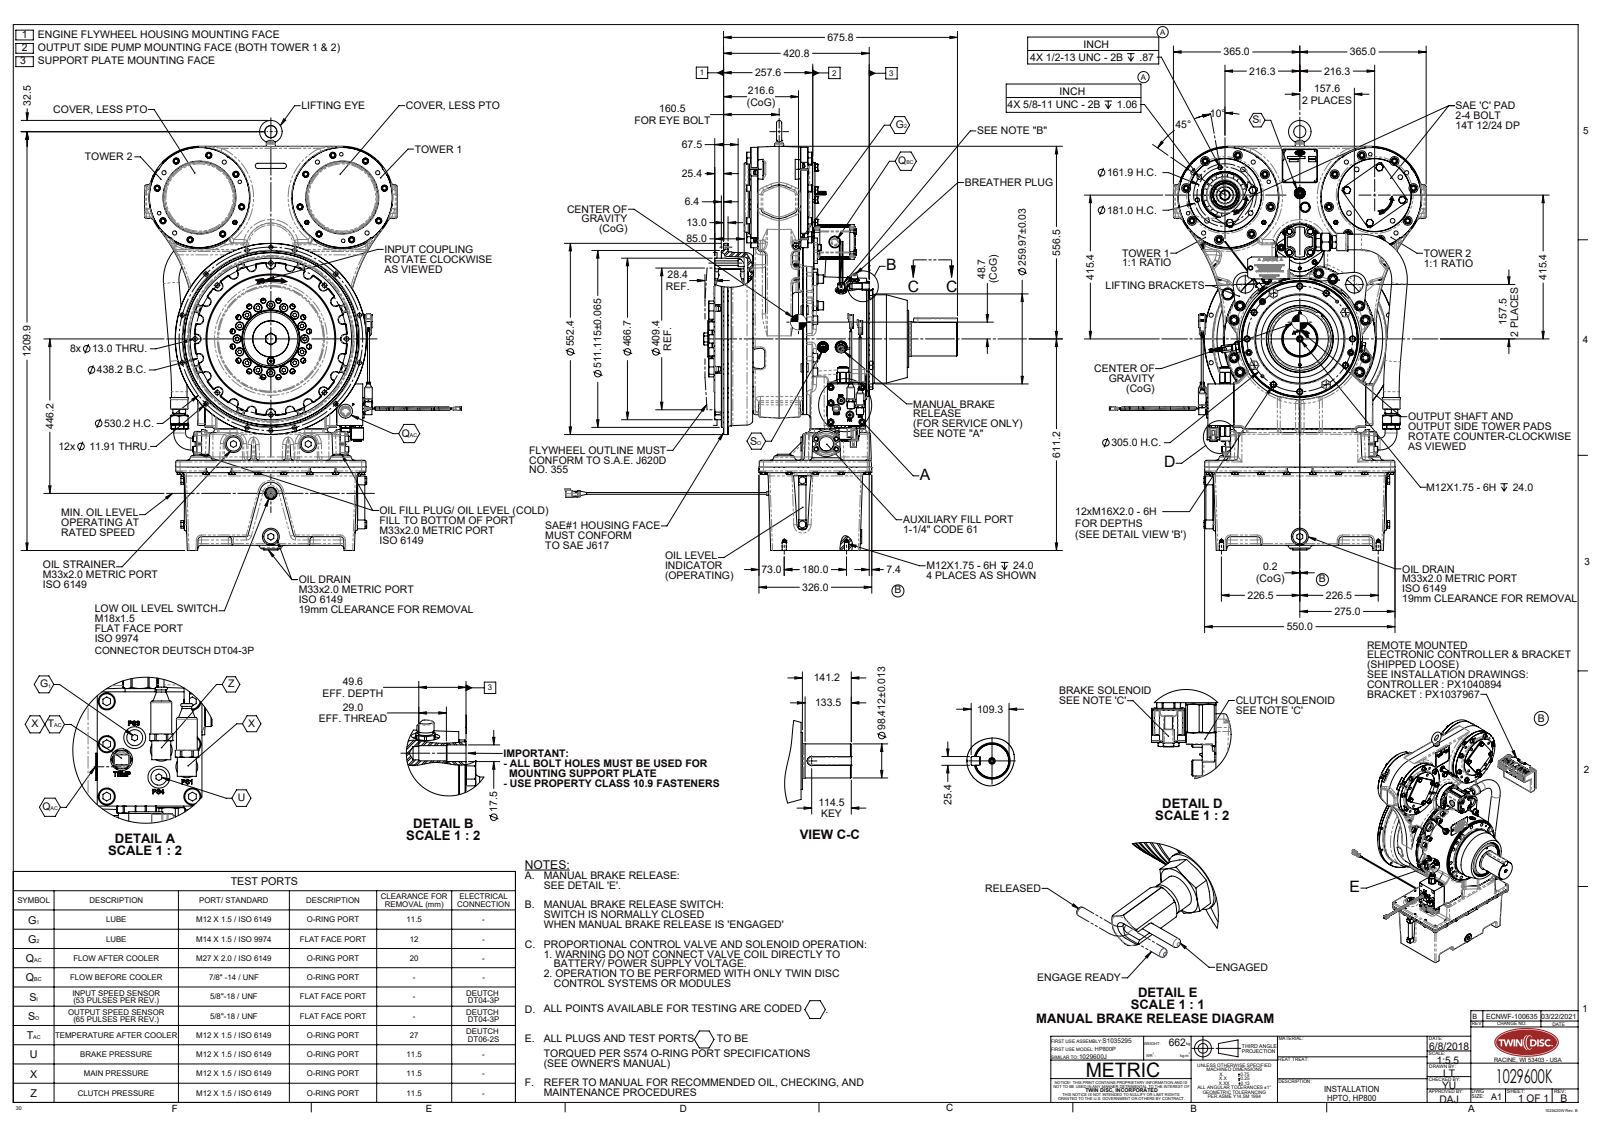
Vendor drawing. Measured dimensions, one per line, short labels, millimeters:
name: 1029600K
written by: SolidWorks 2019 (AUTOMOTIVE_DESIGN)
unit: mm
bodies: 0 solids, 3873 faces (1777 planar, 1091 cylindrical, 1005 other)
size: 1242.39 × 1134.48 × 915.08
holes: 22× ⌀14, 20× ⌀8.5, 18× ⌀24, 14× ⌀26, 12× ⌀11.91, 12× ⌀17.5, 9× ⌀18, 8× ⌀10.2, 8× ⌀12.03, 8× ⌀13, 8× ⌀13.49, 7× ⌀30
bosses: 18× ⌀18, 13× ⌀24, 8× ⌀16, 6× ⌀40.8, 5× ⌀18.87, 4× ⌀16.66, 3× ⌀45, 3× ⌀30.15
rounds: 110× R10, 107× R5, 65× R2.54, 30× R3, 28× R12.7, 11× R1, 11× R1.27, 11× R12.5
face distances: 0.6, 20.6, 7, 141.12, 123.52, 10.6, 130.52, 17.6, 14, 20
hole spacings: 75, 225, 375, 150, 309.23, 86.1, 112.5, 159.1
